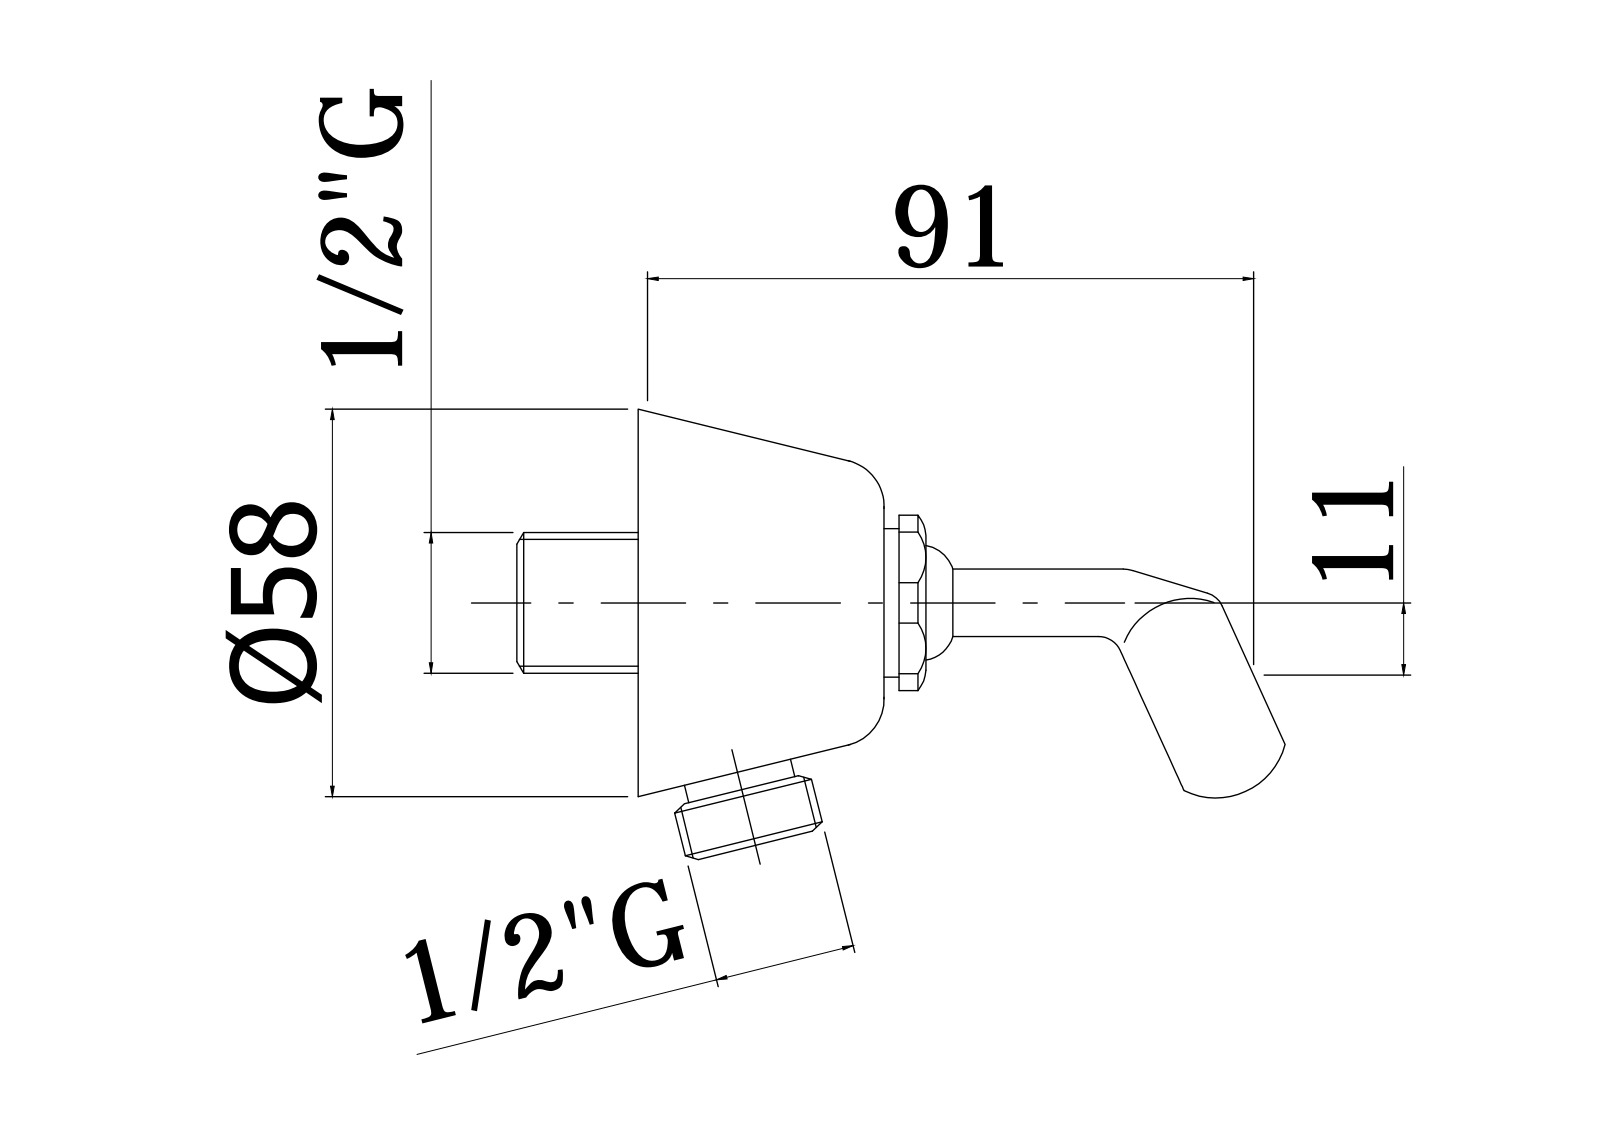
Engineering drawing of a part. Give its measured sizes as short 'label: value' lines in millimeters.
name: ZSUP012CR
written by: CREO PARAMETRIC BY PTC INC, 2020044 (CONFIG_CONTROL_DESIGN)
unit: mm
bodies: 1 solid, 141 faces (43 planar, 42 cylindrical, 56 other)
size: 102.97 × 68.24 × 58.7
volume: 49 820 mm³; area: 23 042 mm²
holes: 1× ⌀6.5, 1× ⌀8, 1× ⌀11, 1× ⌀15, 1× ⌀17, 1× ⌀18
bosses: 1× ⌀27, 1× ⌀22, 1× ⌀21.5, 1× ⌀21, 1× ⌀16.5, 1× ⌀8
rounds: 6× R0.3, 1× R6.5, 1× R11, 1× R14.5
face distances: 7, 33, 40, 13, 20, 2.25, 22, 2, 9, 16
